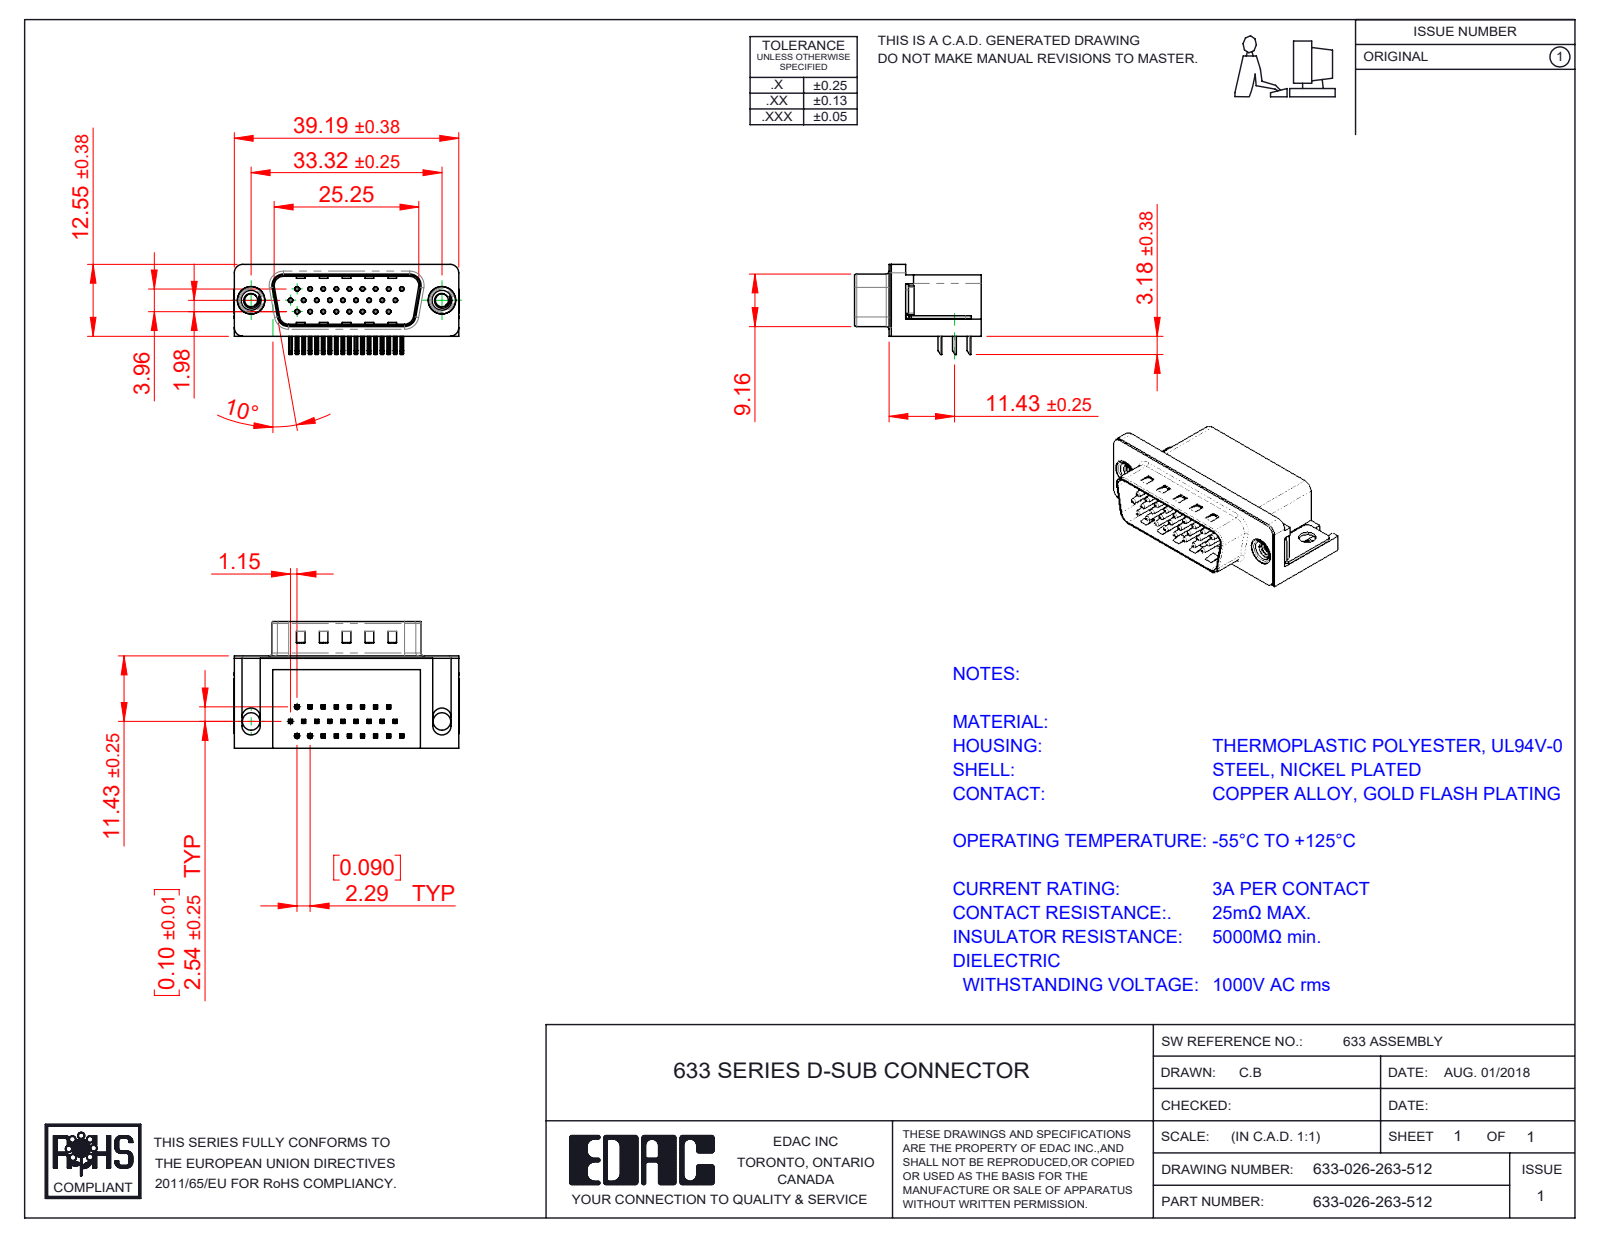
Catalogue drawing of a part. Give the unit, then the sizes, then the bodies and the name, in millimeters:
Units: millimetres
Overall size (bounding box): 39.22 × 22.1 × 15.73
Round holes (diameter × count): ⌀0.35 ×26, ⌀0.8 ×26, ⌀2.26 ×2, ⌀3.05 ×2, ⌀4 ×2, ⌀4.8 ×2, ⌀5 ×2
Round bosses / shafts (diameter × count): ⌀0.75 ×26, ⌀4.9 ×2, ⌀4.75 ×2, ⌀3.9 ×2
Partial cylindrical surfaces — rounded edges, fillets, slot ends (radius × count): R0.25 ×112, R0.12 ×52, R1 ×16, R0.5 ×9, R1.5 ×8, R1.6 ×8, R0.9 ×4, R2 ×4
Main face-to-face distances: 0.4, 10.35, 15.7, 2.9, 2.5, 16.1, 0.5, 8.76, 0.35, 10.7
Hole centre spacings: 2.29, 4.57, 2.28, 3.96, 6.05, 4.58, 6.86, 7.92
Volume: 5 597 mm³ · Surface area: 7 238 mm²
Bodies: 32 solids, 2302 faces (1419 planar, 678 cylindrical, 205 other)
Part name (STEP PRODUCT): 633 Contact Middle; 633 Contact Top; 633 Contact Bottom; 633 Housing_26 Contact (+4 more)
STEP written by: SolidWorks 2016 (CONFIG_CONTROL_DESIGN)
